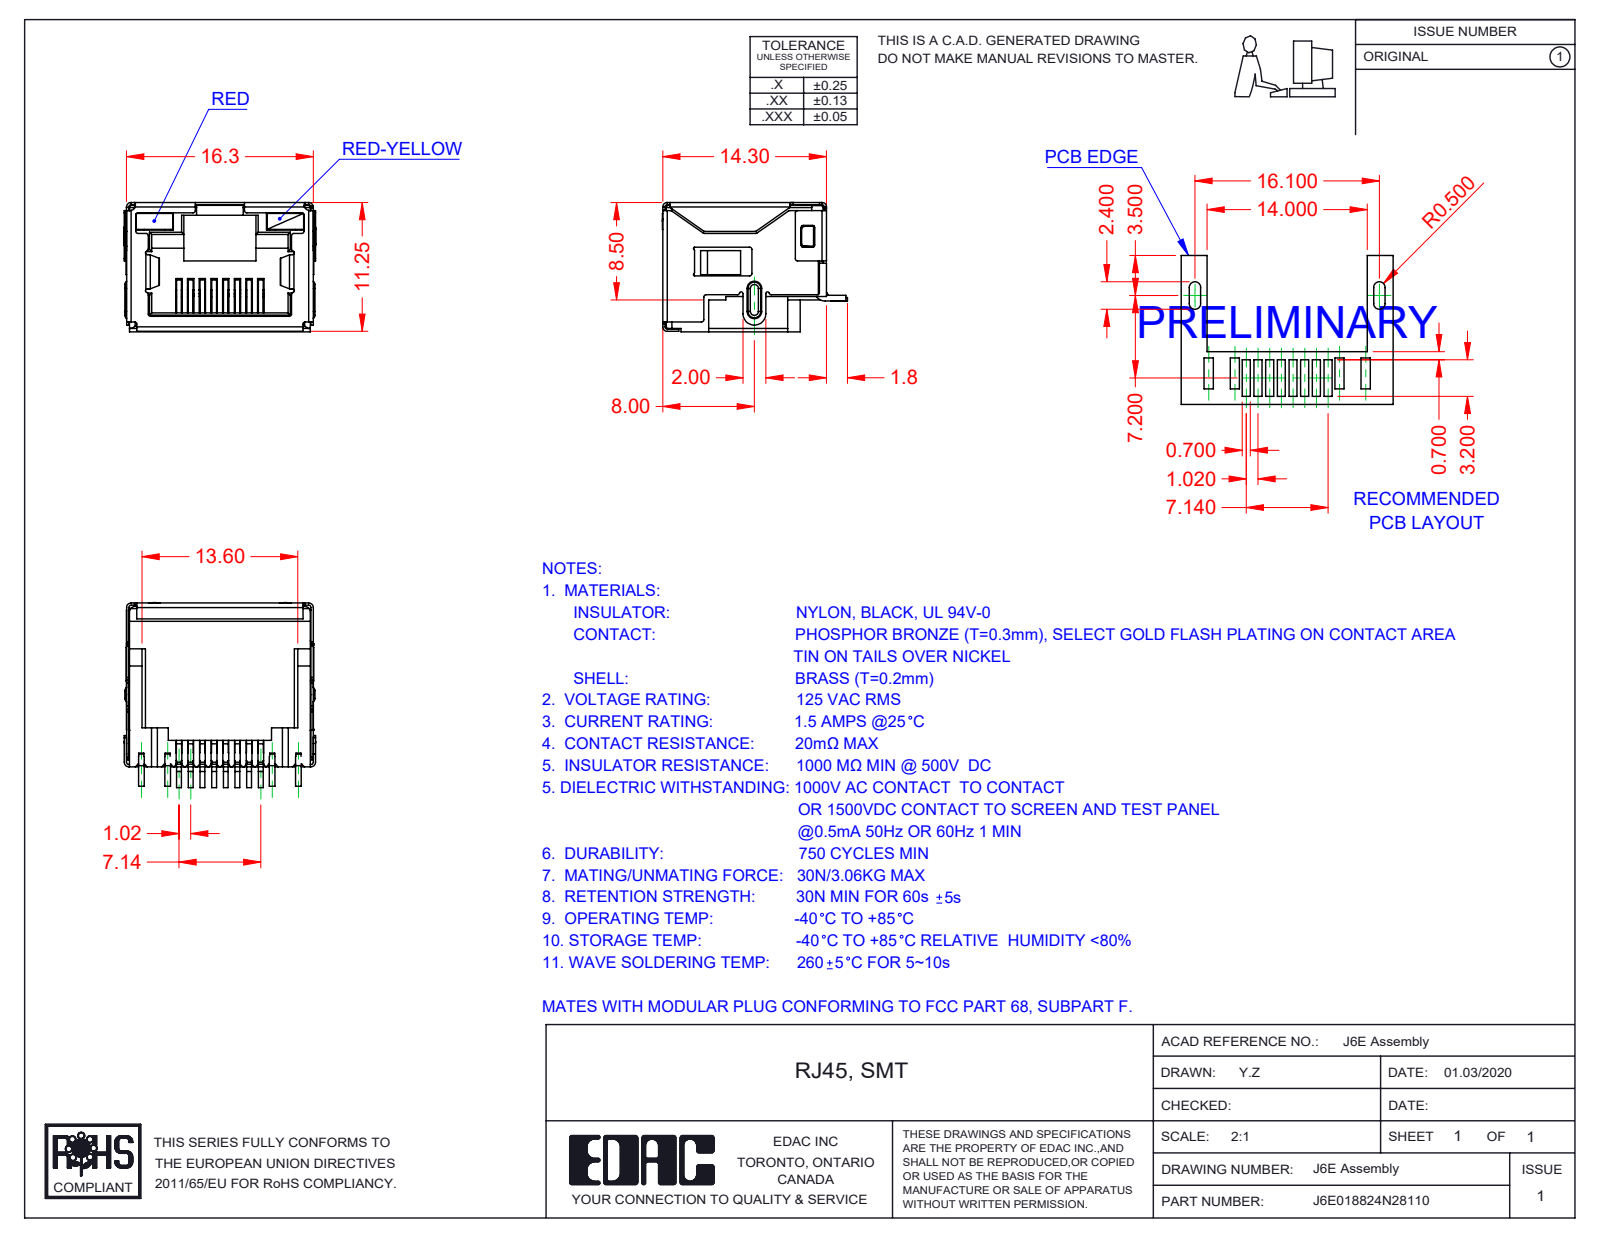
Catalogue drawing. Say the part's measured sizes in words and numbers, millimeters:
The part is named "J6E018824N28110; 6E LED RH_8-Red-Yellow; 6E Insulator_LED; 6E Shield_LED (+2 more)". Its 3-D file was written by "SolidWorks 2016 (CONFIG_CONTROL_DESIGN)". It is 12 solids with 1498 faces: 1099 planar, 349 cylindrical and 50 other. Overall it measures 16.75 by 16.15 by 11.3 millimeters. Its volume is 1 109 cubic millimeters and its surface area 4 045 square millimeters. Partial cylindrical surfaces (rounded edges, fillets, slot ends): 82 of radius 0.2, 17 of radius 0.25, 13 of radius 0.4, 13 of radius 0.5, 10 of radius 0.1, 7 of radius 0.15, 4 of radius 0.3, 3 of radius 1. The main face-to-face distances are 11.05, 16.05, 16.1, 15.85, 11.1, 11.3, 2.4, 0.7, 9.85, 0.49.
